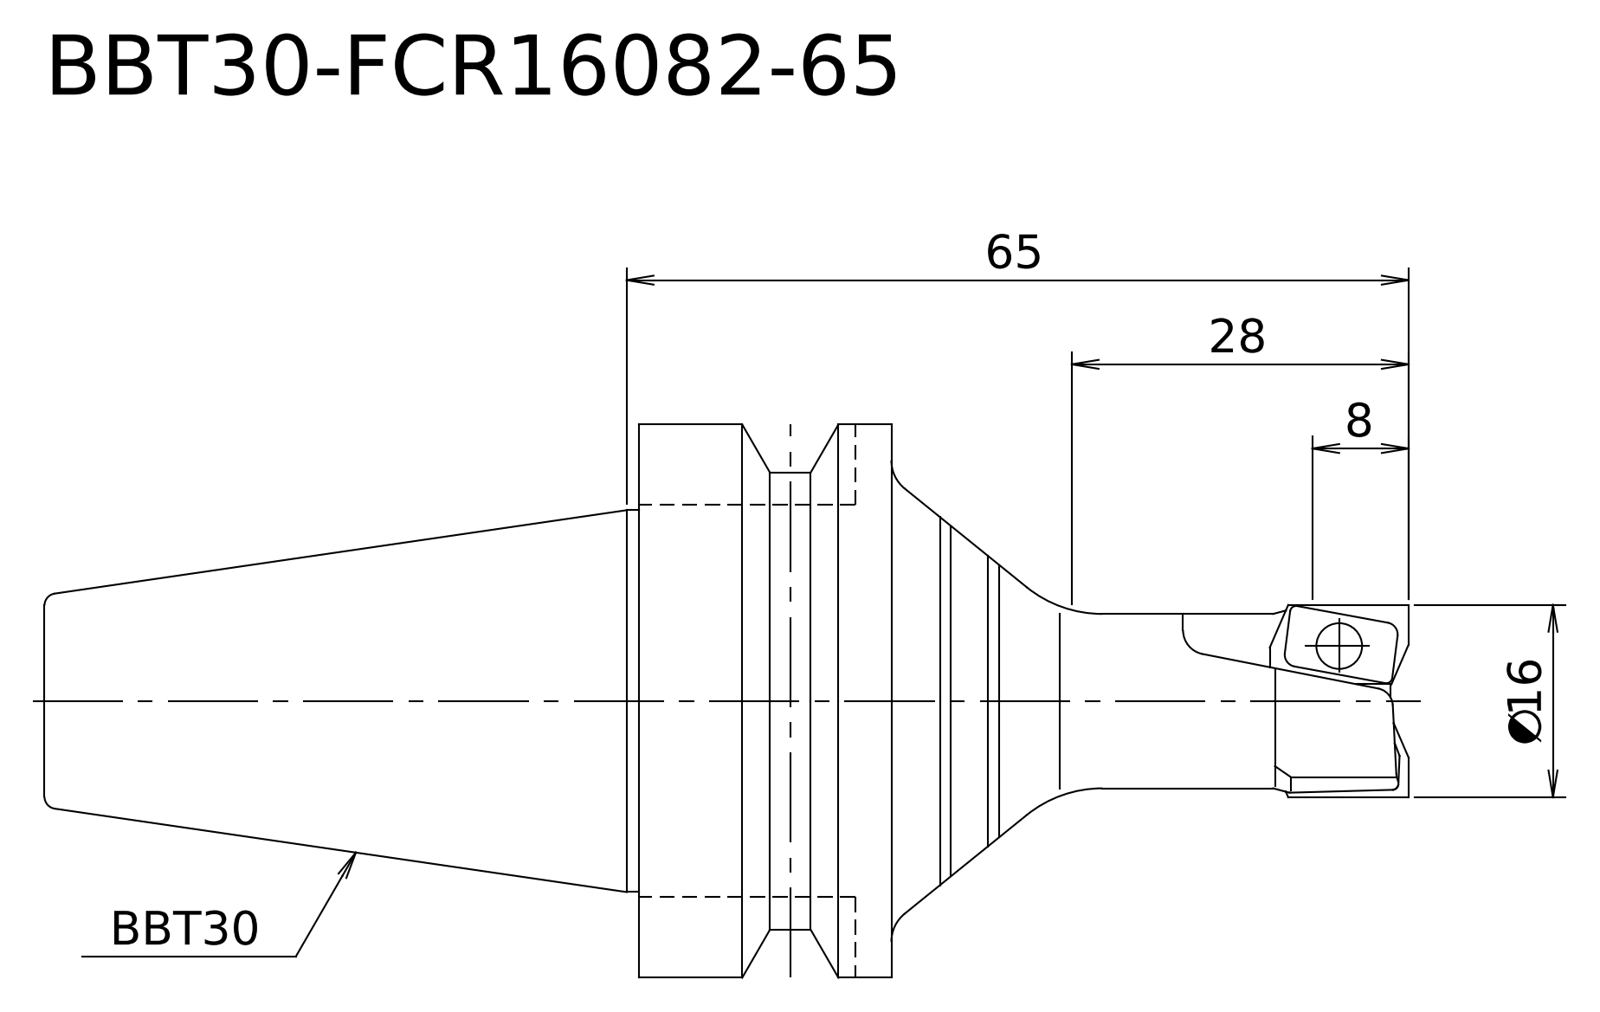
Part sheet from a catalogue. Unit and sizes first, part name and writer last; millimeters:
Units: millimetres
Overall size (bounding box): 113.4 × 46 × 46
Round bosses / shafts (diameter × count): ⌀46 ×1, ⌀38 ×1, ⌀31.75 ×1, ⌀16 ×1, ⌀14.5 ×1
Main face-to-face distances: 21, 70.4, 49.4, 43, 64, 113.4
Volume: 69 678 mm³ · Surface area: 12 093 mm²
Bodies: 1 solid, 17 faces (4 planar, 6 cylindrical, 7 other)
STEP written by: Kubotek KeyCreator V8.5.1 (14335) (CONFIG_CONTROL_DESIGN)
